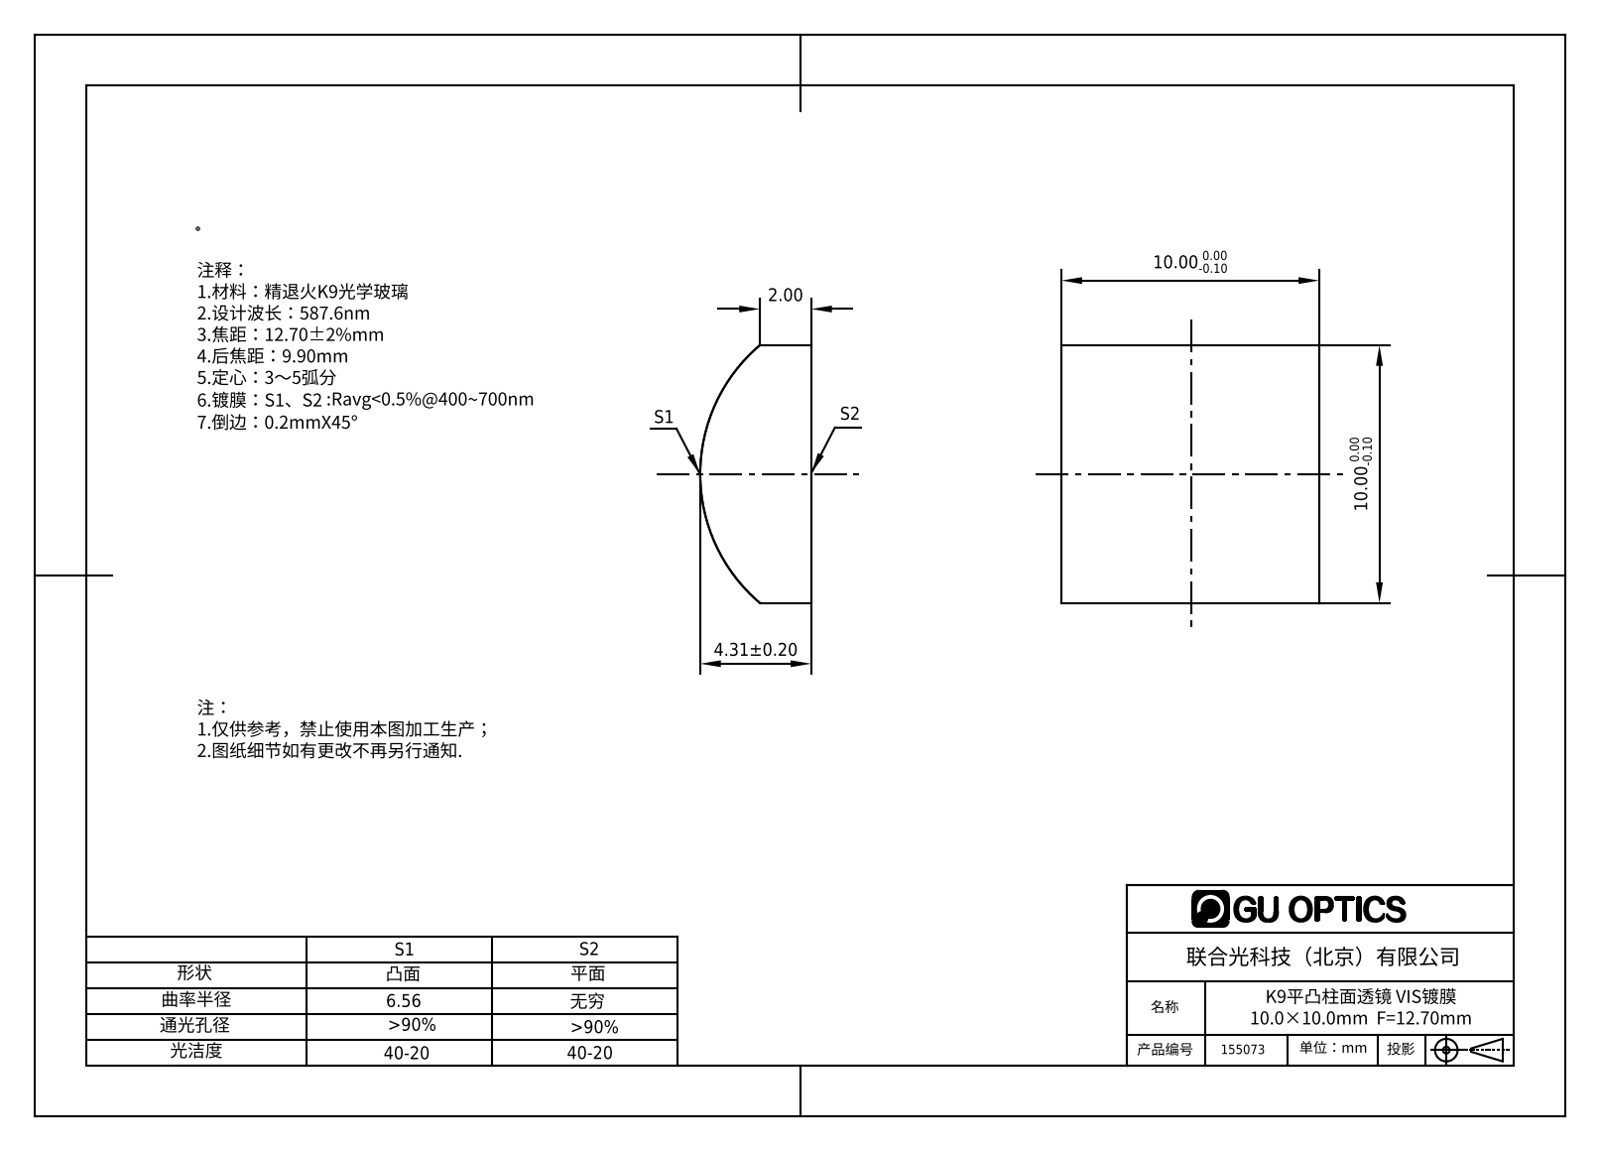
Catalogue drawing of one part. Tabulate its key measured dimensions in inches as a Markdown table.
| quantity | value |
| --- | --- |
| part name | 155007 |
| STEP written by | SolidWorks 2016 (AUTOMOTIVE_DESIGN) |
| units | inches |
| bodies | 1 solid, 6 faces (5 planar, 1 cylindrical, 0 other) |
| overall size | 0.394 × 0.394 × 0.17 |
| volume | 0.022 in³ |
| surface area | 0.505 in² |
| partial cylindrical surfaces (radius × count) | 0.258 × 1 |
| main face-to-face distances | 0.394 |
